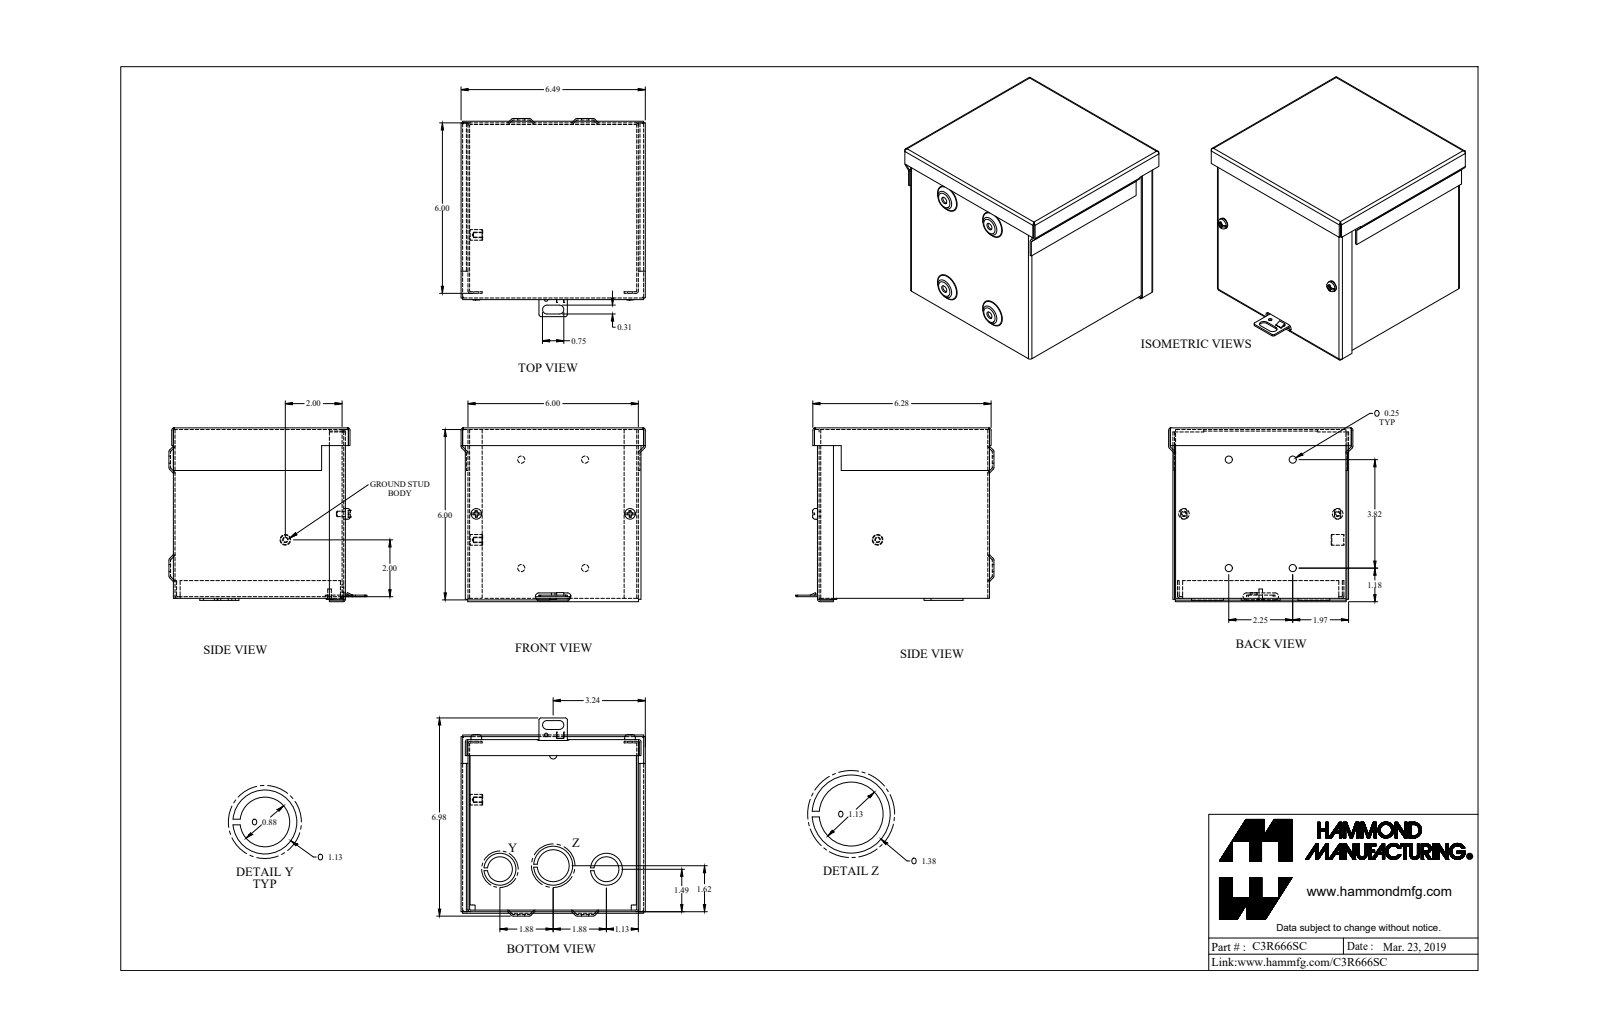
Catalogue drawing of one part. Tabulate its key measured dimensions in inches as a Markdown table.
| quantity | value |
| --- | --- |
| part name | C3R666SC_Default |
| STEP written by | SolidWorks 2019 (CONFIG_CONTROL_DESIGN) |
| units | inches |
| bodies | 9 solids, 357 faces (182 planar, 101 cylindrical, 74 other) |
| overall size | 6.977 × 6.489 × 6.12 |
| volume | 15.53 in³ |
| surface area | 551.6 in² |
| round holes (diameter × count) | 0.17 × 4, 0.25 × 4, 0.875 × 2, 0.125 × 1, 0.137 × 1, 0.156 × 1, 1.125 × 1 |
| round bosses / shafts (diameter × count) | 0.375 × 3, 1.125 × 2, 0.19 × 2, 1.375 × 1, 0.125 × 1 |
| partial cylindrical surfaces (radius × count) | 0.029 × 21, 0.086 × 21, 0.125 × 8, 0.109 × 4, 0.156 × 2 |
| main face-to-face distances | 0.057, 6, 5.943, 0.057, 5.886, 6.057, 5.886, 5.943, 0.114, 0.244 |
| hole center spacings | 2.48, 4.281, 2.25, 2.782, 3.818, 4.431, 0.763, 1.13 |
